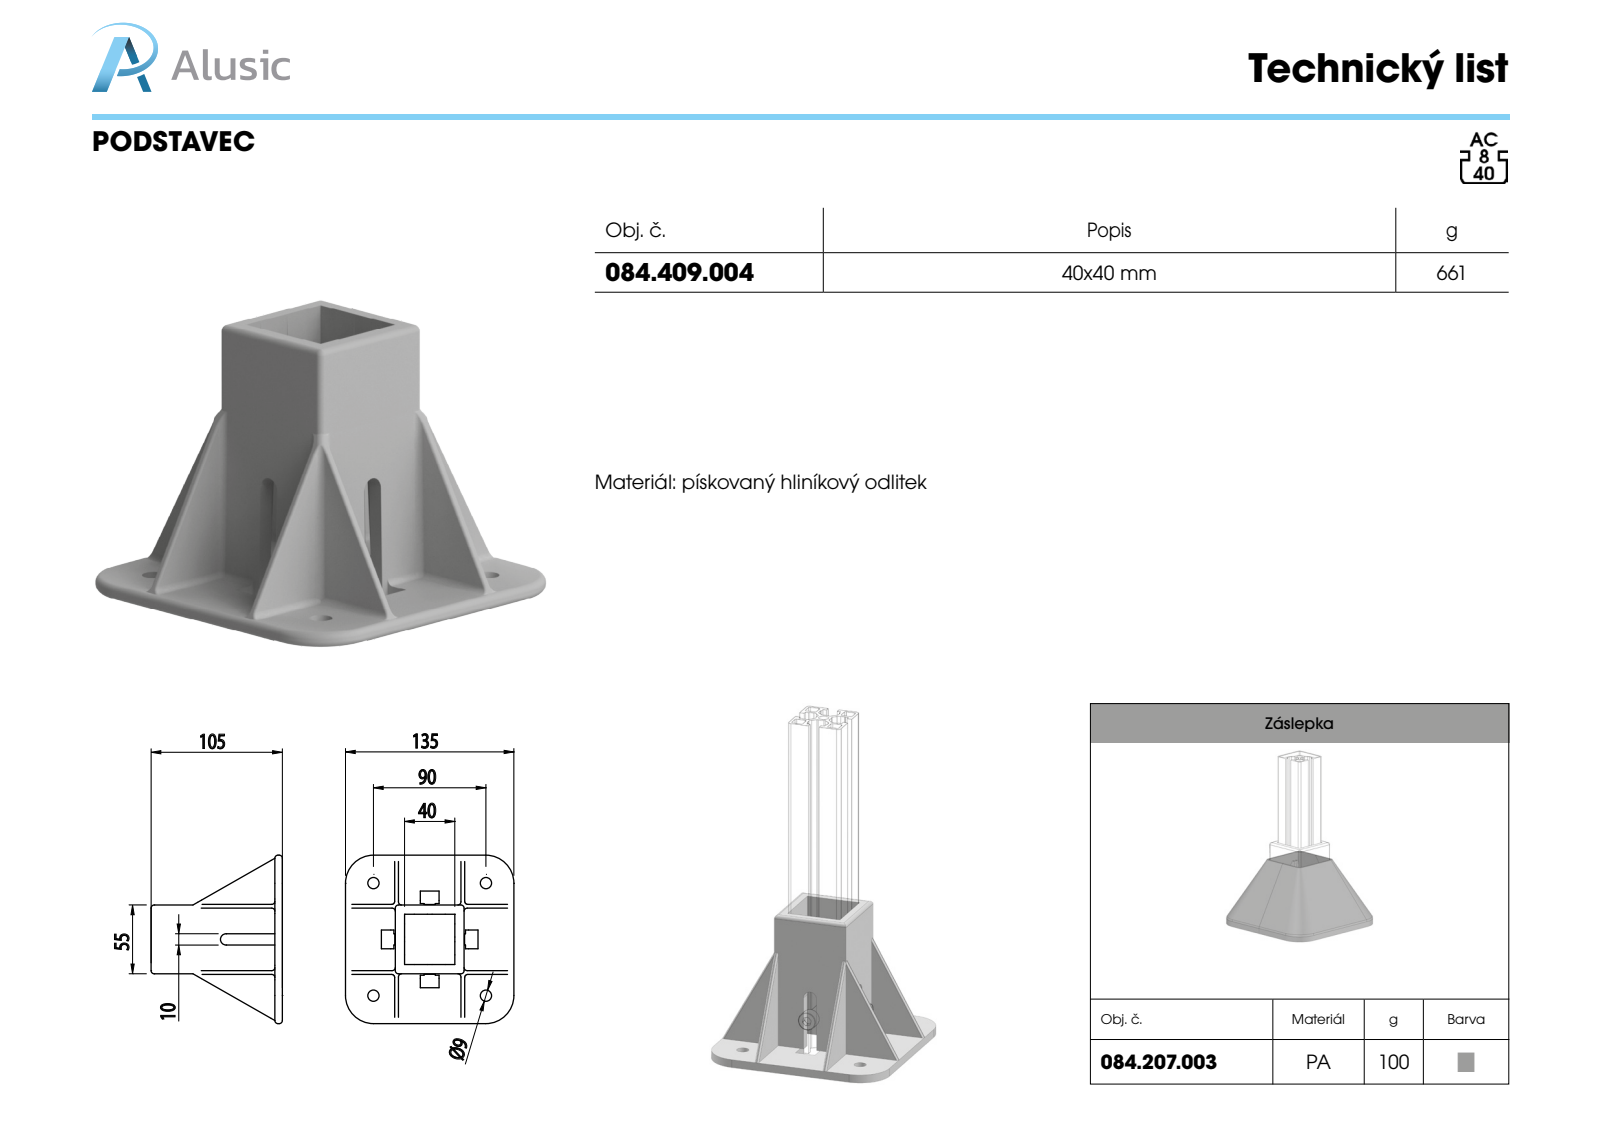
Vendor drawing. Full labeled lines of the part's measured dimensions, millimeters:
Part name (STEP PRODUCT): 084.409.004
STEP written by: SolidWorks 2011 (CONFIG_CONTROL_DESIGN)
Units: millimetres
Bodies: 1 solid, 110 faces (74 planar, 36 cylindrical, 0 other)
Overall size (bounding box): 135 × 135 × 105
Volume: 251 354 mm³ · Surface area: 94 058 mm²
Round holes (diameter × count): ⌀9 ×4
Partial cylindrical surfaces — rounded edges, fillets, slot ends (radius × count): R1.2 ×16, R2.5 ×4, R22.5 ×4, R5 ×2
Main face-to-face distances: 47.5, 7.5, 55, 6, 3, 52, 4.5, 44.5, 40, 49
Hole centre spacings: 90, 127.28
